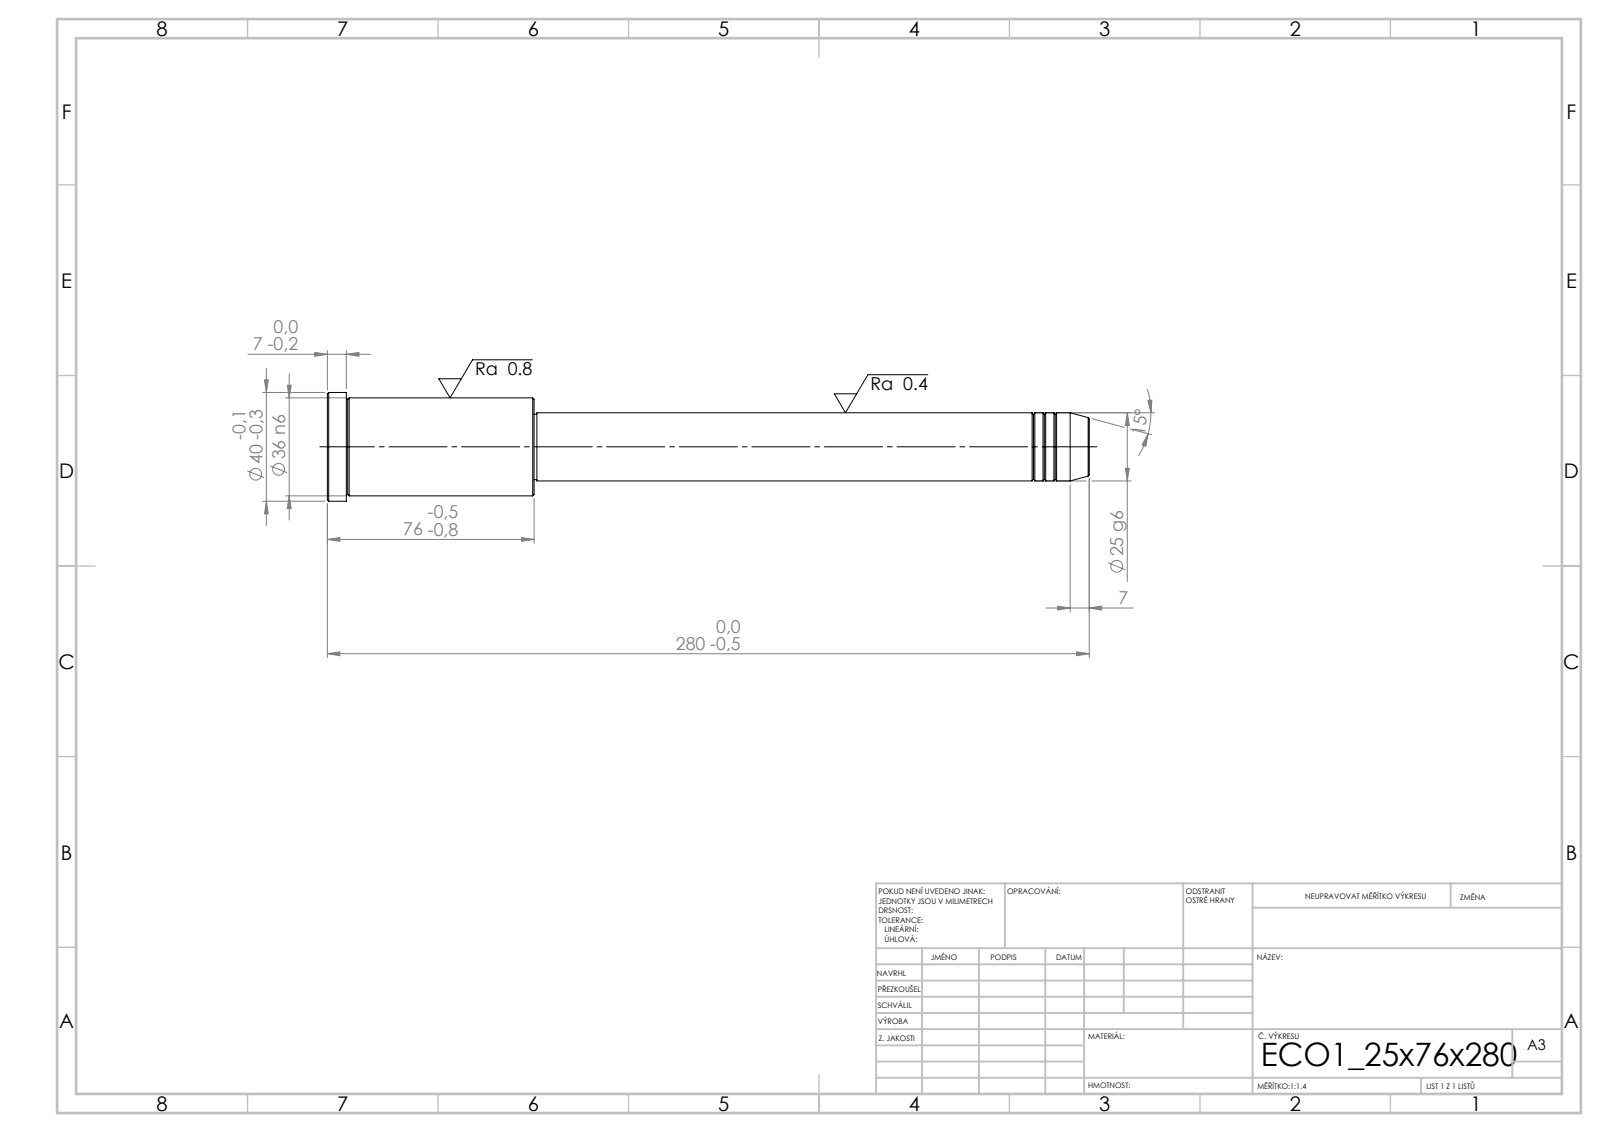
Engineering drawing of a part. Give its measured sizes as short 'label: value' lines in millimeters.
written by: SolidWorks 2019 (CONFIG_CONTROL_DESIGN)
unit: mm
bodies: 1 solid, 43 faces (5 planar, 14 cylindrical, 24 other)
size: 280 × 40 × 40
volume: 178 474 mm³; area: 27 241 mm²
bosses: 1× ⌀40, 1× ⌀36, 1× ⌀25, 1× ⌀24
face distances: 76, 204, 280, 273, 69, 7, 203, 1, 70, 77
